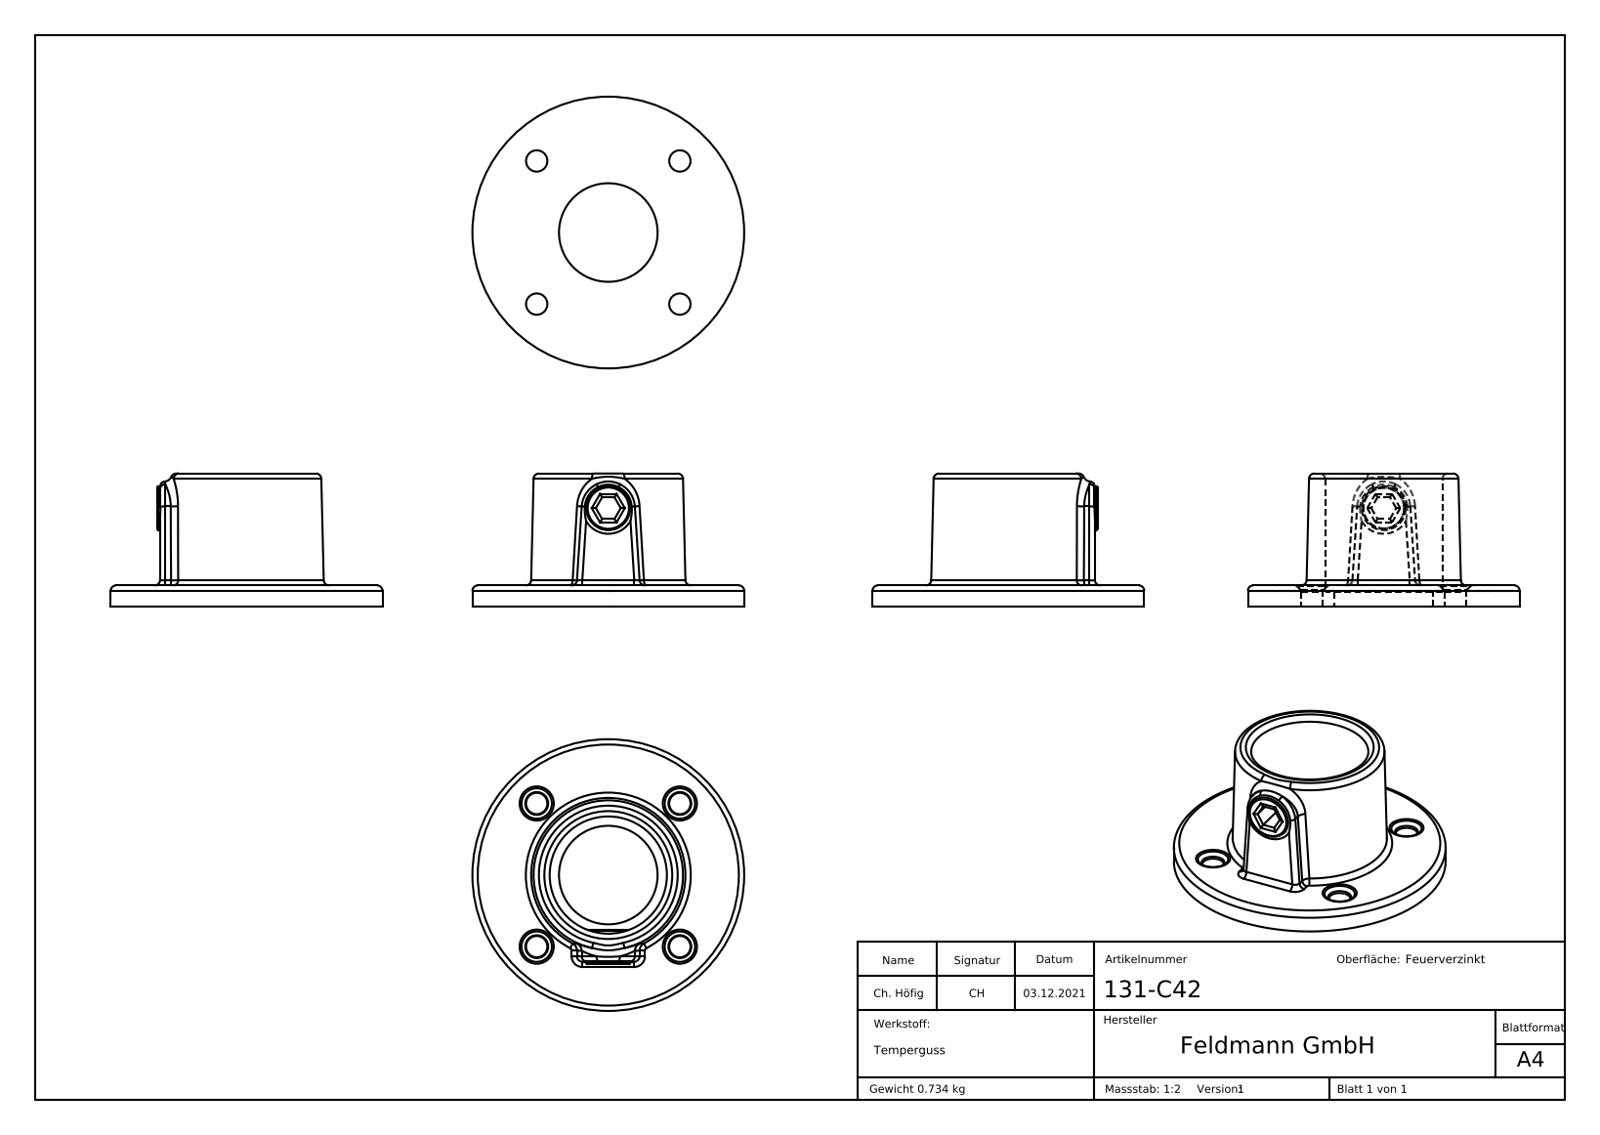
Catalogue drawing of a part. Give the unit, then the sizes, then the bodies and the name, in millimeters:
Units: millimetres
Overall size (bounding box): 102 × 102 × 50
Round holes (diameter × count): ⌀8 ×4, ⌀15.25 ×1, ⌀37 ×1, ⌀44 ×1
Round bosses / shafts (diameter × count): ⌀102 ×1, ⌀16.5 ×1
Partial cylindrical surfaces — rounded edges, fillets, slot ends (radius × count): R2 ×17, R10 ×1
Main face-to-face distances: 8, 5.5, 2.5, 50, 44.5, 42, 8.1, 12, 13, 1
Hole centre spacings: 38, 53.74, 76
Volume: 100 397 mm³ · Surface area: 32 198 mm²
Bodies: 2 solids, 74 faces (15 planar, 28 cylindrical, 31 other)
Part name (STEP PRODUCT): 131-C42 Teil2; 131-C42 Teil1; 131-C42
STEP written by: SolidWorks 2018 (CONFIG_CONTROL_DESIGN)
